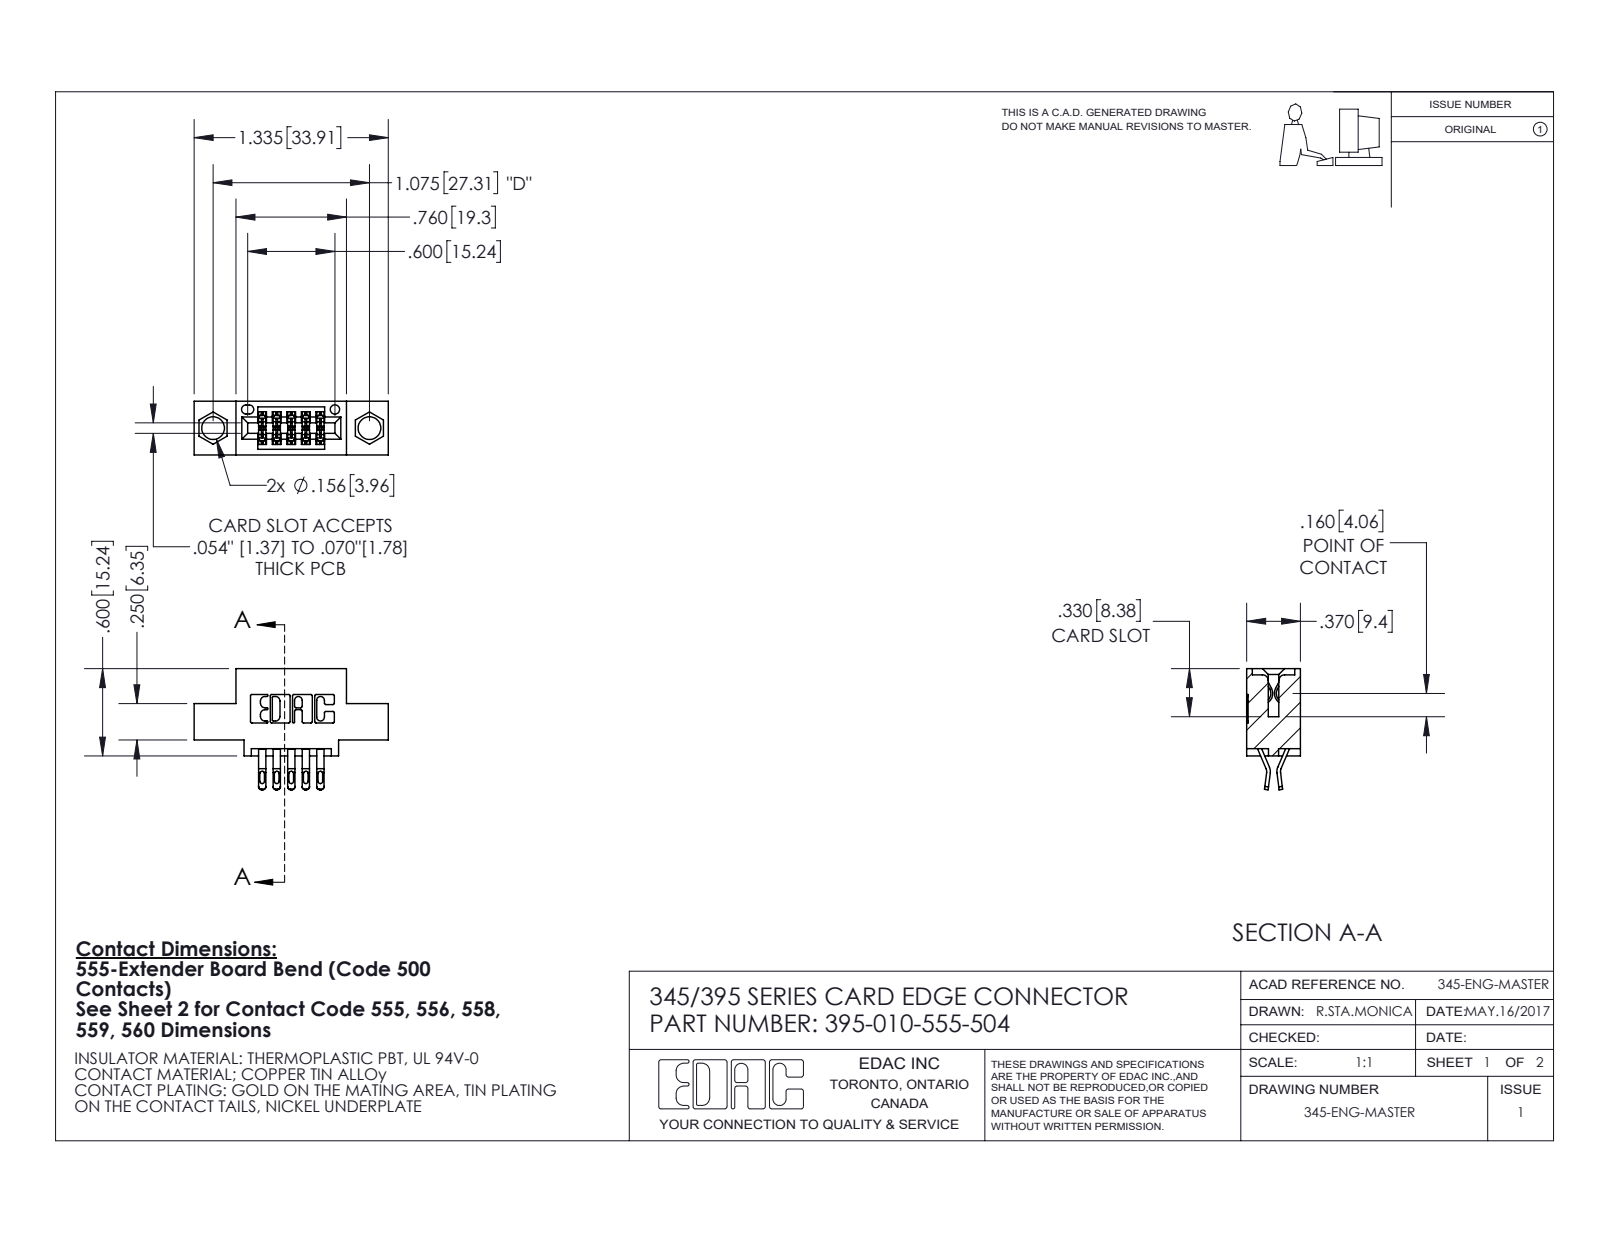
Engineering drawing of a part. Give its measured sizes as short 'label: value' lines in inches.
name: 345 Part_0.110 Offset - 0.156 Dia-TI; 395-010-555-504; 345-292-001_555 Tail
written by: SolidWorks 2020 (CONFIG_CONTROL_DESIGN)
unit: in
bodies: 11 solids, 704 faces (408 planar, 296 cylindrical, 0 other)
size: 1.335 × 0.832 × 0.37
volume: 0.171 in³; area: 5.375 in²
holes: 2× ⌀0.156, 1× ⌀0.064
rounds: 25× R0.016, 22× R0.01, 20× R0.006, 20× R0.02, 6× R0.007, 6× R0.031, 3× R0.026, 2× R0.01
face distances: 0.2, 0.37, 0.1, 0.298, 0.072, 0.25, 0.025, 0.098, 0.272, 0.06
hole spacings: 0.27, 0.847, 1.075
